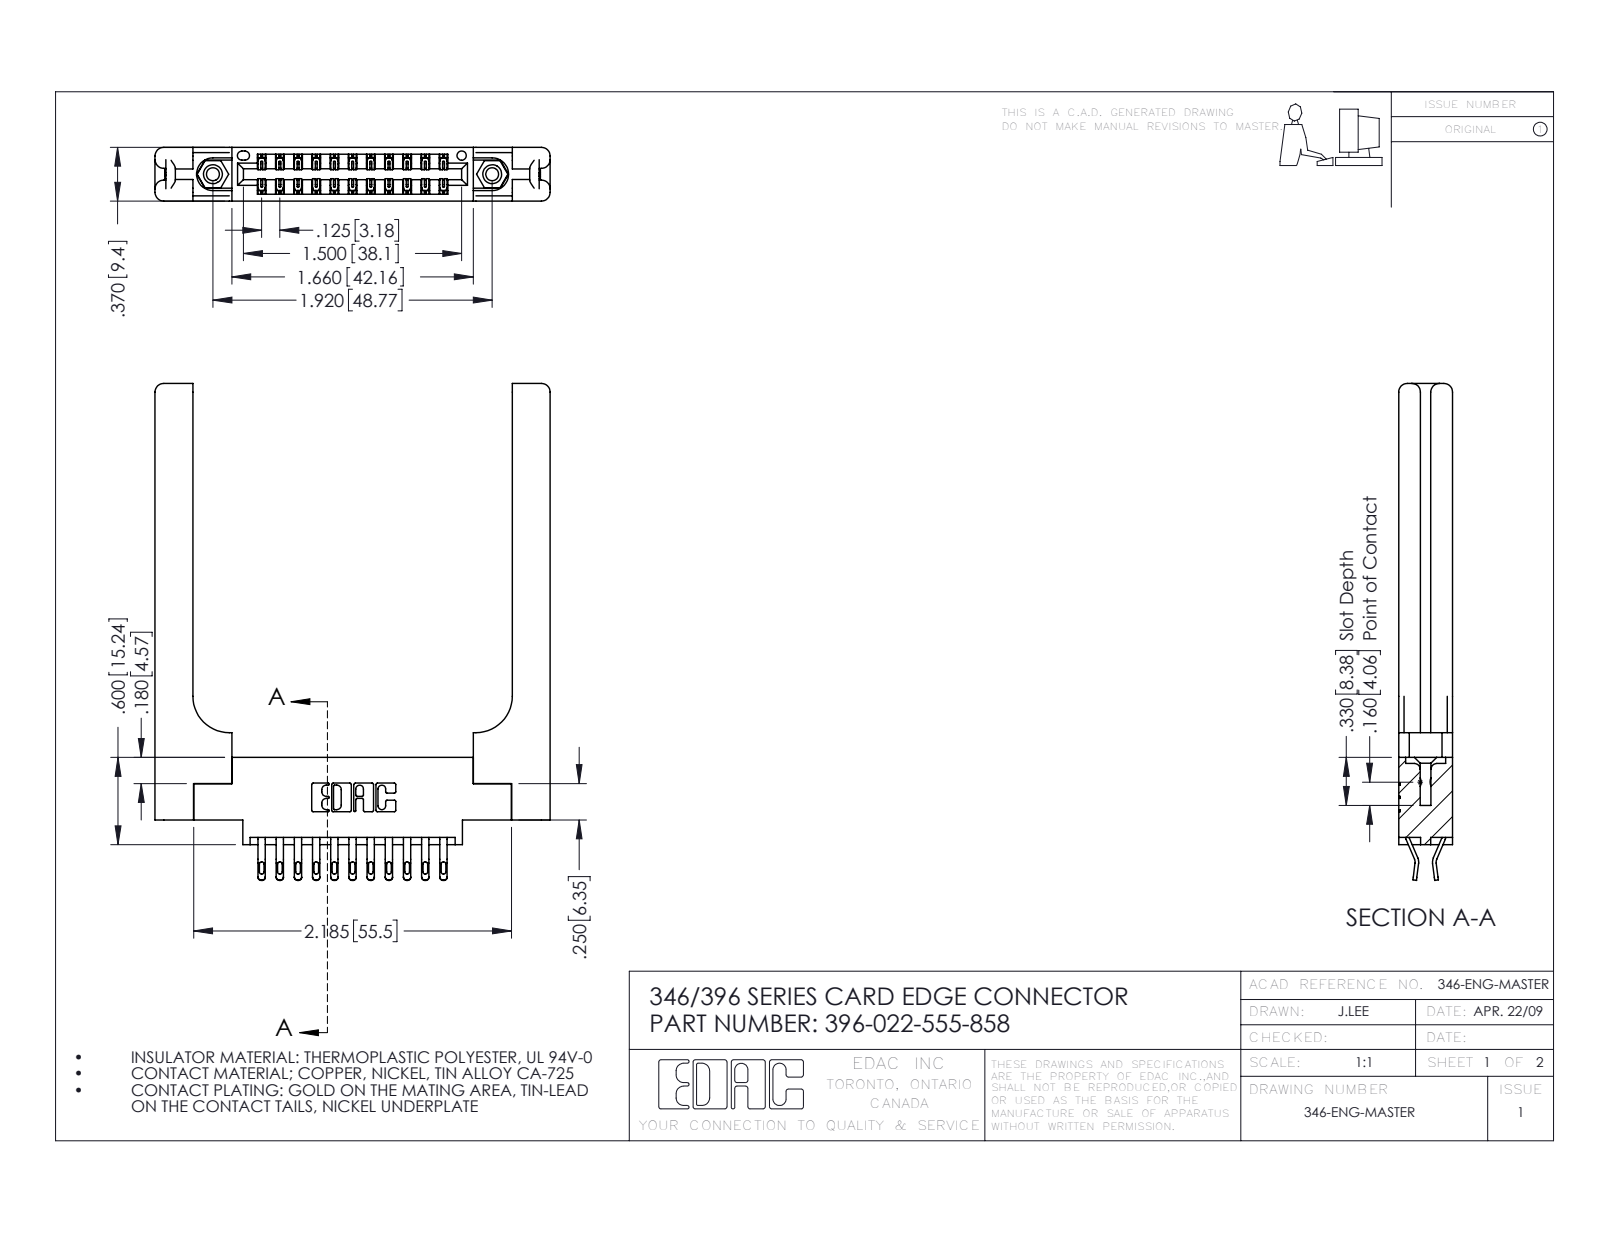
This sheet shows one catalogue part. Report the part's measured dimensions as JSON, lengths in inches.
{"part_name": "345-292-001_555 Tail; 346 Part_0.170 Offset - 0.156 Dia-TH; 345-250-001_345-250-001-102; 346-220-058_345-220-058 (+1 more)", "step_written_by": "SolidWorks 2016 (CONFIG_CONTROL_DESIGN)", "units": "inches", "bodies": {"solids": 27, "faces": 1658, "planar": 954, "cylindrical": 644, "other": 60}, "overall_size": [3.415, 2.716, 0.37], "volume_in3": 0.848, "surface_area_in2": 21.21, "round_holes": [[0.089, 2], [0.125, 2], [0.156, 2], [0.064, 1]], "round_bosses_or_shafts": [[0.155, 2]], "partial_cylinders_radius": [[0.016, 44], [0.02, 44], [0.006, 33], [0.01, 22], [0.06, 16], [0.007, 6], [0.031, 6], [0.026, 3]], "face_to_face_distances": [0.37, 0.15, 0.072, 0.148, 0.22, 0.102, 0.048, 0.322, 0.173, 0.25], "hole_center_spacings": [0.246, 1.715, 1.92]}
